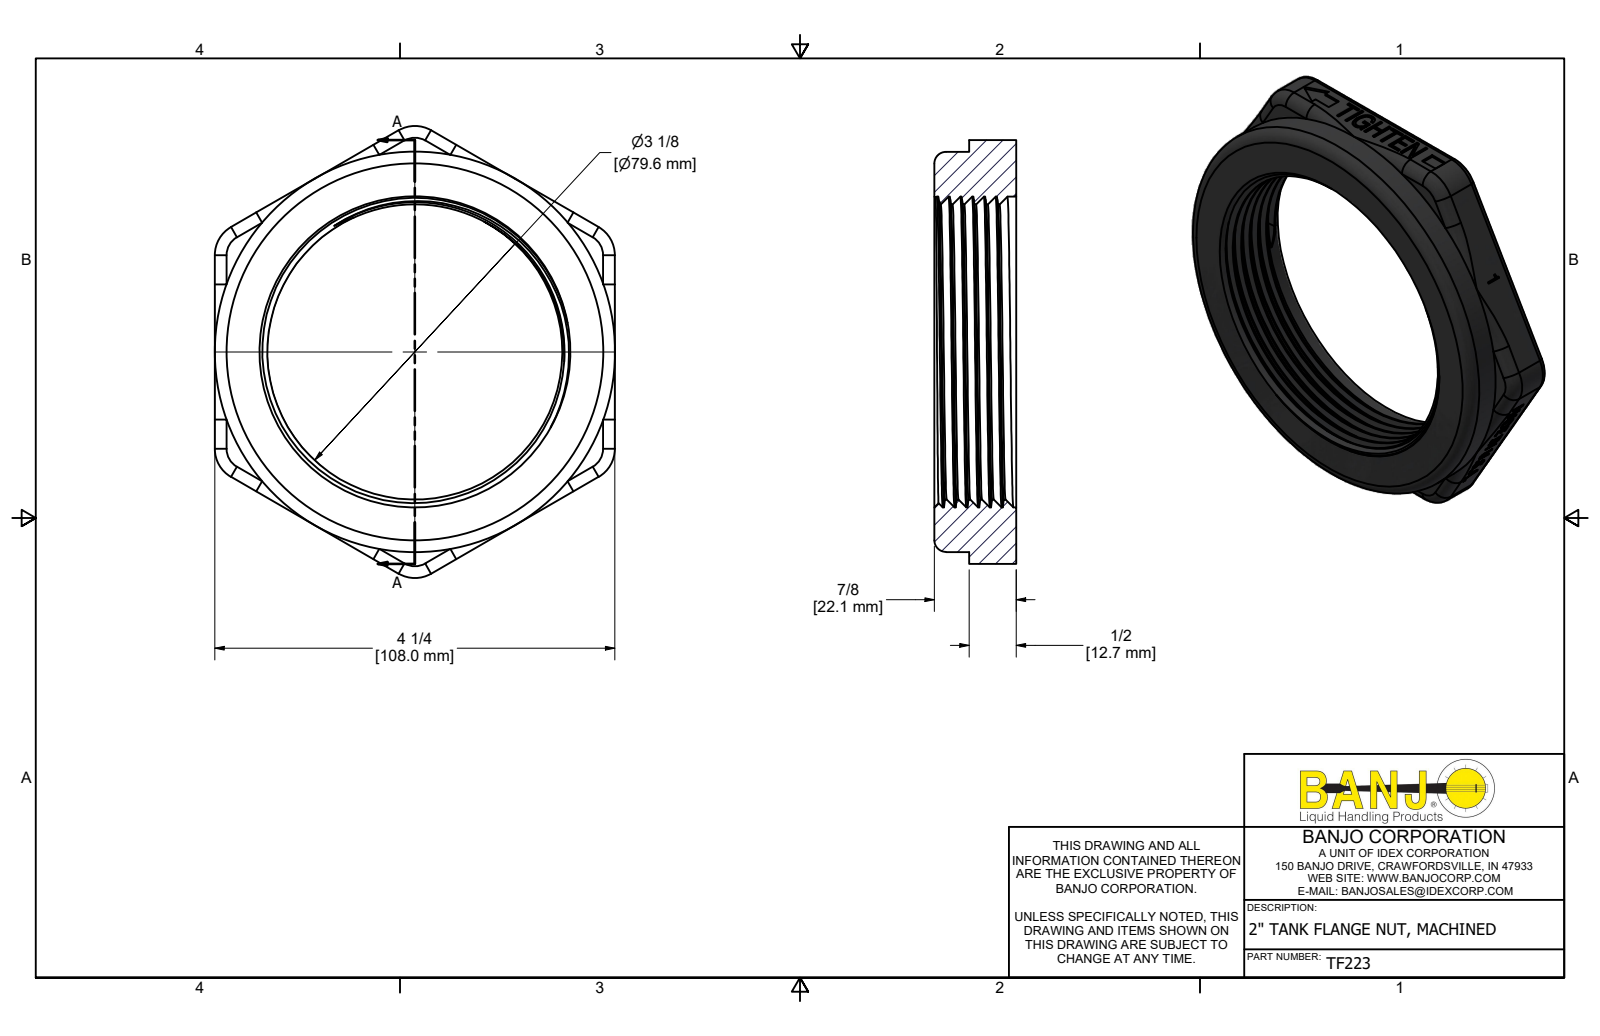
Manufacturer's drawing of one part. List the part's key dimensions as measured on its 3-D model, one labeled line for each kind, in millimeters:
Part name (STEP PRODUCT): TF223; TF223X
STEP written by: Autodesk Inventor 2022 (AUTOMOTIVE_DESIGN)
Units: millimetres
Bodies: 1 solid, 505 faces (341 planar, 40 cylindrical, 124 other)
Overall size (bounding box): 121.9 × 108 × 22.1
Volume: 95 650 mm³ · Surface area: 26 190 mm²
Round holes (diameter × count): ⌀79.6 ×1, ⌀83.8 ×1
Round bosses / shafts (diameter × count): ⌀108 ×1
Partial cylindrical surfaces — rounded edges, fillets, slot ends (radius × count): R1.6 ×6, R3.2 ×6, R8.7 ×6, R22.1 ×1
Main face-to-face distances: 22.1, 108, 0.5, 107.4, 12.7, 9.4, 106.9, 7.9, 20.6, 1.5
